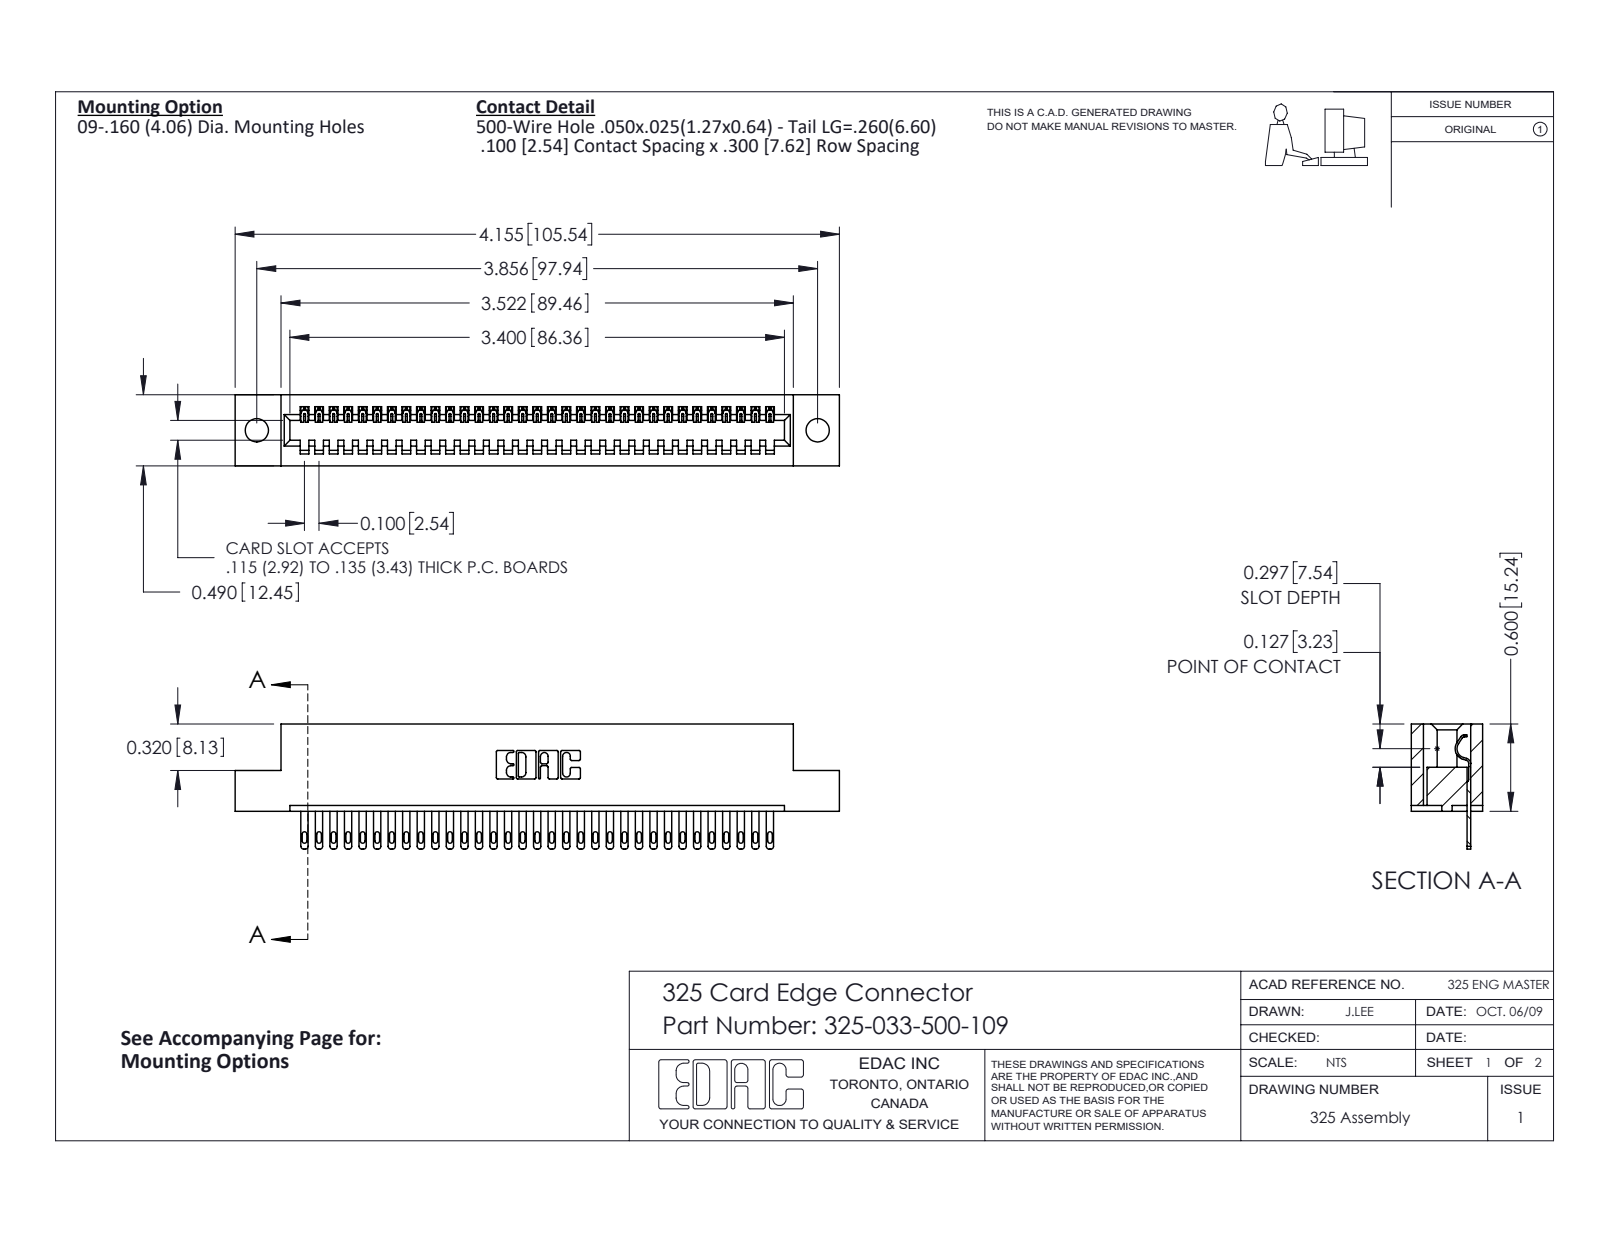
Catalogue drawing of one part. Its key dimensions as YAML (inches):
part_name: "325 Part_.160 TH; 325-292-001_325-293-100; 325-033-500-109"
step_written_by: "SolidWorks 2016 (CONFIG_CONTROL_DESIGN)"
units: inches
bodies: {solids: 34, faces: 1896, planar: 1258, cylindrical: 638, other: 0}
overall_size: [4.155, 0.86, 0.49]
volume: 0.8
surface_area: 21.93
round_holes:
  - {diameter: 0.16, count: 2}
partial_cylinders:
  - {radius: 0.006, count: 66}
  - {radius: 0.016, count: 66}
  - {radius: 0.02, count: 66}
  - {radius: 0.01, count: 22}
  - {radius: 0.007, count: 6}
  - {radius: 0.031, count: 6}
  - {radius: 0.026, count: 3}
  - {radius: 0.014, count: 1}
face_to_face_distances: [0.083, 0.407, 0.49, 0.3, 0.107, 0.383, 0.025, 0.325, 0.56, 0.04]
hole_center_spacings: [3.856]
